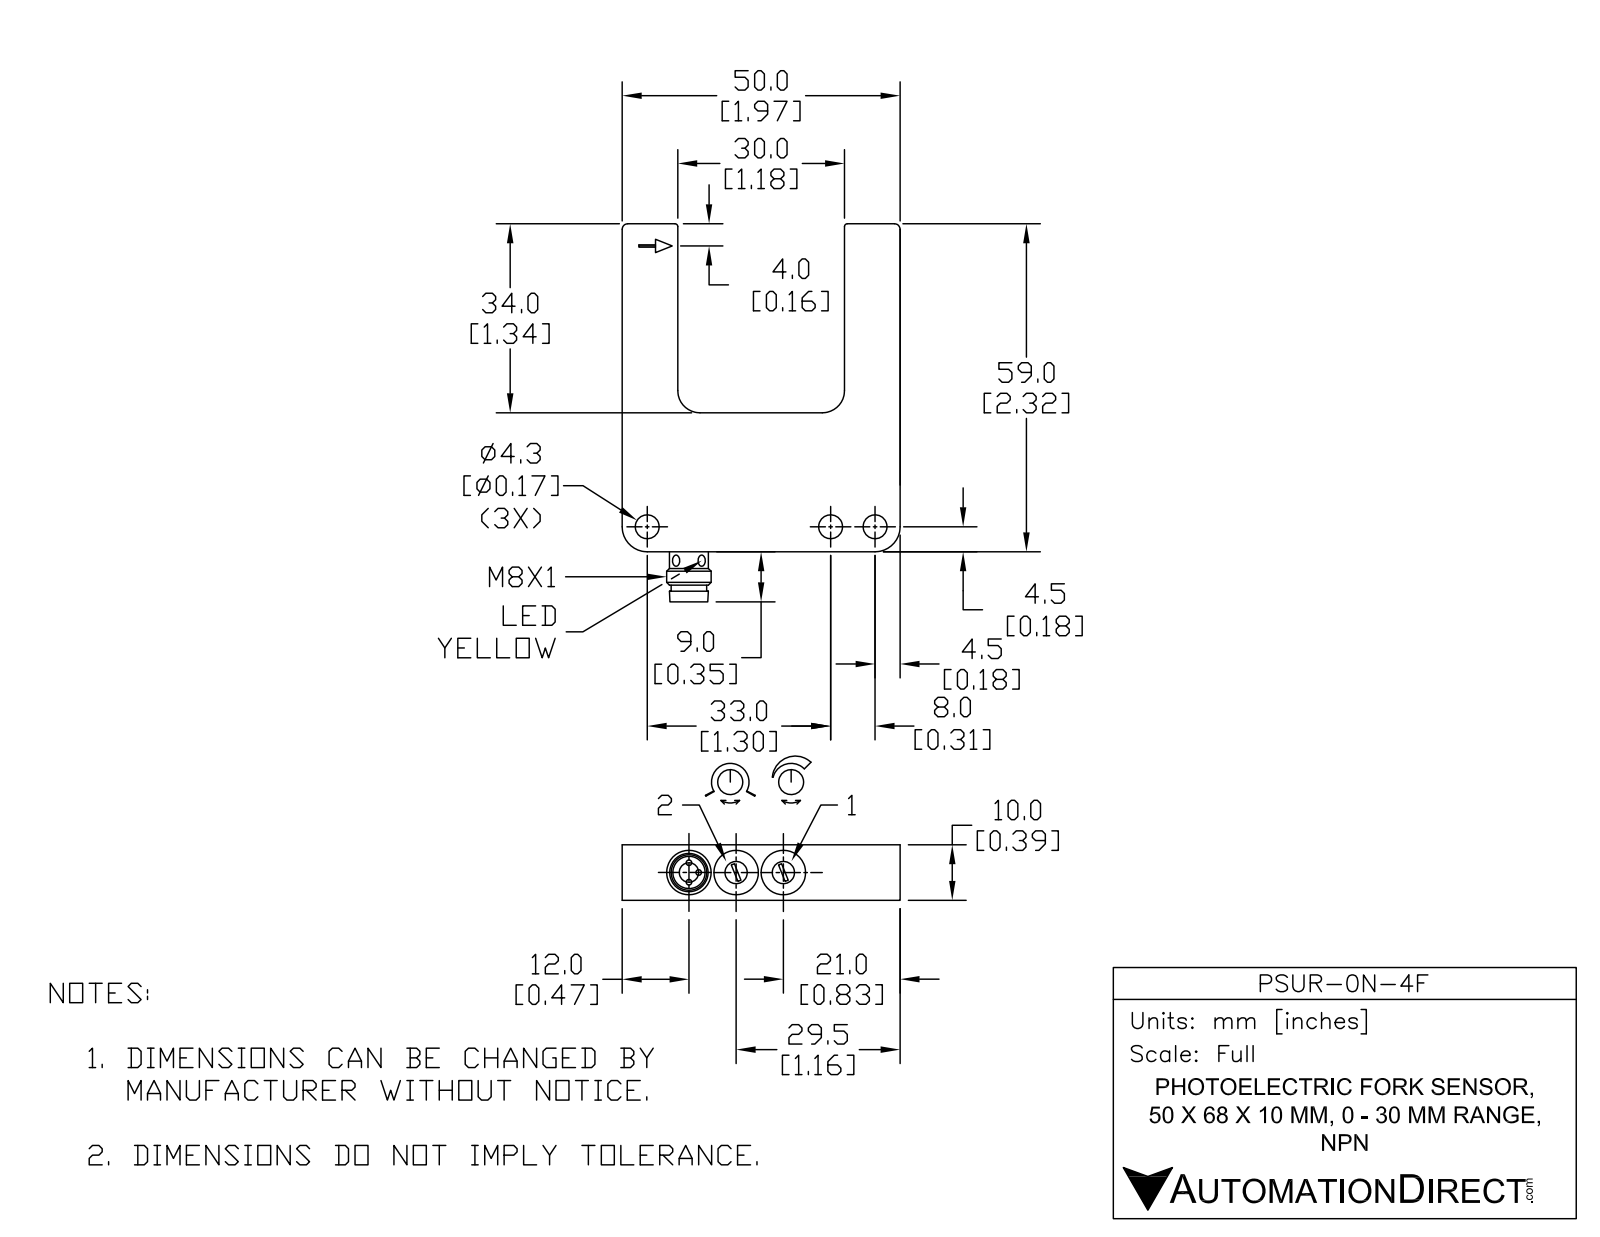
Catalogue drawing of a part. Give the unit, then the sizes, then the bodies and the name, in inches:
Units: inches
Overall size (bounding box): 2.677 × 1.969 × 0.394
Round holes (diameter × count): ⌀0.169 ×3, ⌀0.079 ×2, ⌀0.157 ×2, ⌀0.315 ×2, ⌀0.228 ×1
Round bosses / shafts (diameter × count): ⌀0.315 ×1, ⌀0.267 ×1
Partial cylindrical surfaces — rounded edges, fillets, slot ends (radius × count): R0.02 ×2, R0.039 ×2, R0.063 ×2, R0.157 ×2, R0.177 ×2
Main face-to-face distances: 0.394, 1.575, 1.969, 1.181, 0.984, 1.339, 2.323, 2.319, 0.98, 0.157
Hole centre spacings: 0.335, 0.315, 0.669, 1.299, 1.614
Volume: 1.162 in³ · Surface area: 11.28 in²
Bodies: 1 solid, 83 faces (35 planar, 42 cylindrical, 6 other)
Part name (STEP PRODUCT): PSUR-0N-4F
STEP written by: SolidWorks 2016 (AUTOMOTIVE_DESIGN)
